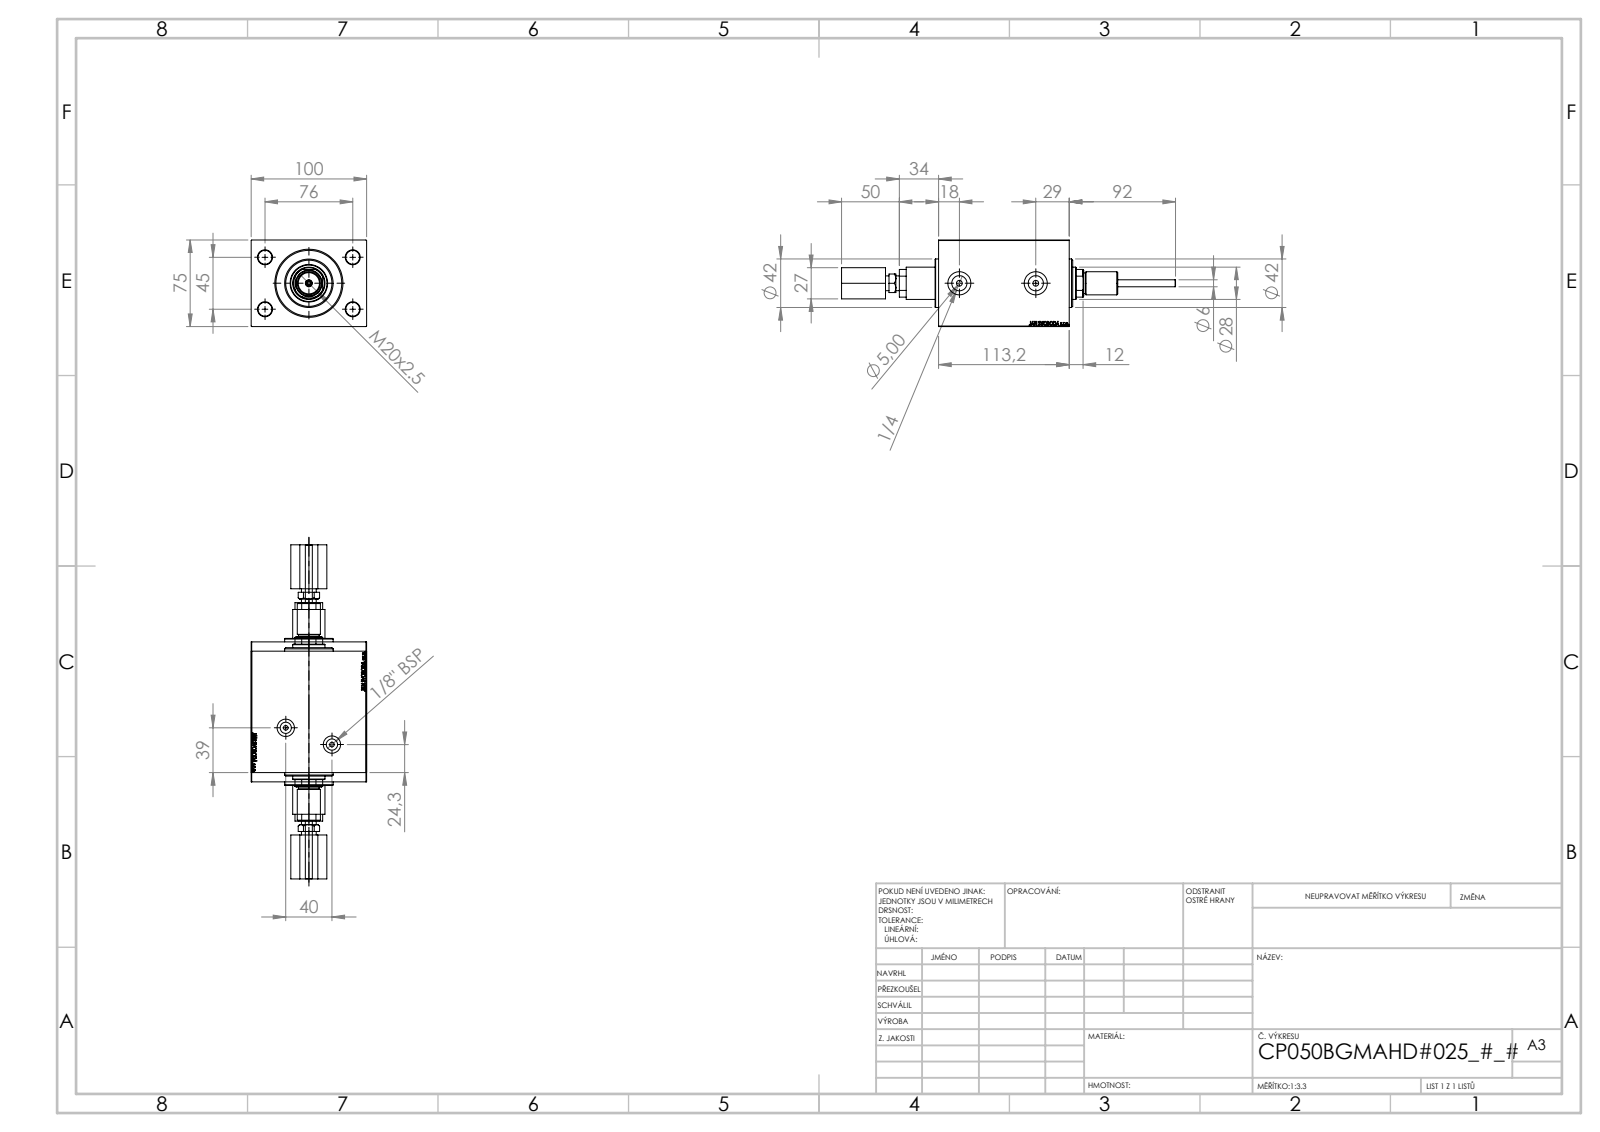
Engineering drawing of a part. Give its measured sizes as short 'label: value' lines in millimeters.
name: V450DCP_VC_B; V450DCP_B_VCP; V450DCP_B_Body; V450DCP_B_RodCooling_ACCESSORIES (+1 more)
written by: SolidWorks 2019 (CONFIG_CONTROL_DESIGN)
unit: mm
bodies: 5 solids, 986 faces (438 planar, 98 cylindrical, 450 other)
size: 289.2 × 100 × 75
volume: 849 166 mm³; area: 132 649 mm²
holes: 4× ⌀12, 2× ⌀4, 2× ⌀5, 2× ⌀9.73, 2× ⌀13.16, 2× ⌀15, 2× ⌀20, 1× ⌀3, 1× ⌀6, 1× ⌀18.5, 1× ⌀28, 1× ⌀31.5
bosses: 1× ⌀42, 1× ⌀20, 1× ⌀18, 1× ⌀12.78
rounds: 1× R13.5
face distances: 75, 100, 113.2, 14, 99.2, 43, 1, 27, 13, 112.2
hole spacings: 44.16, 45, 76, 88.32, 42.55, 66.2
